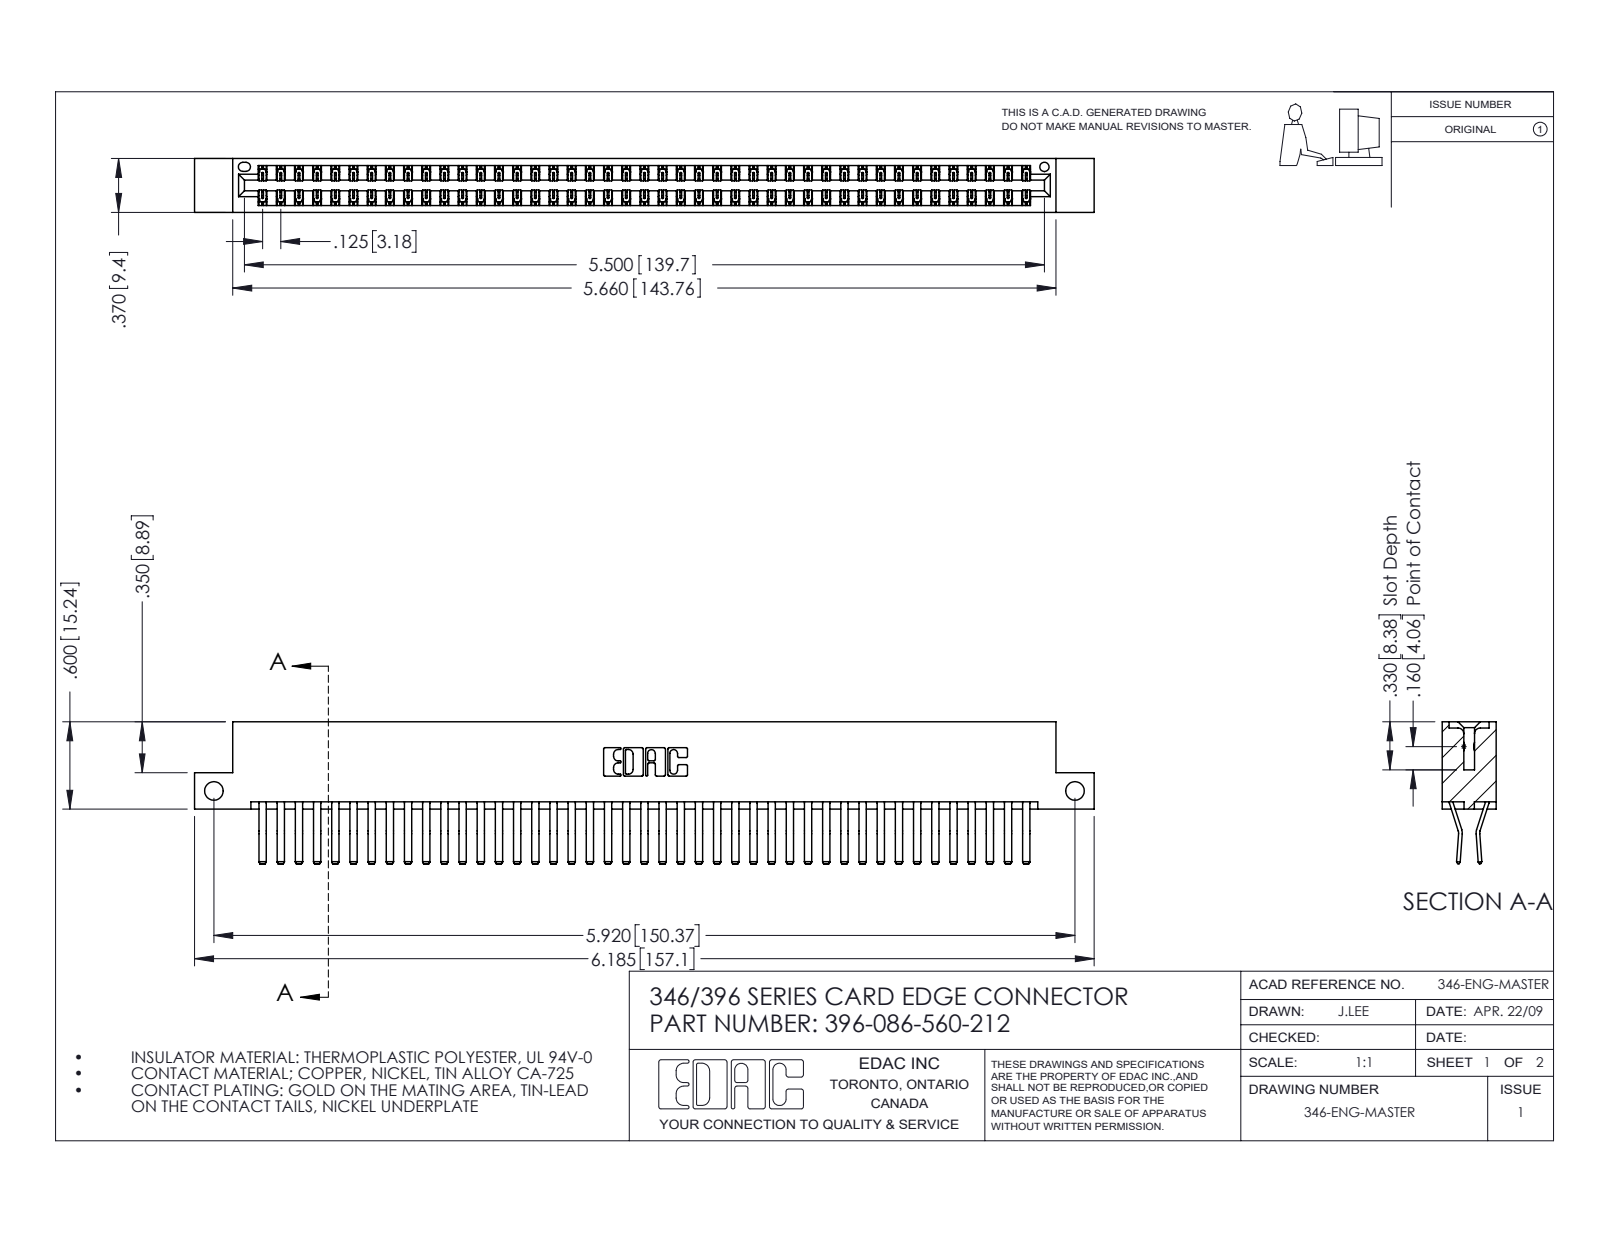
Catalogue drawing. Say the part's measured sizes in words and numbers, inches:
The part is named "396-086-560-212; 345-292-001_560 Tail; 346 Part_Flush Mounting Lugs - Side Mount". Its 3-D file was written by "SolidWorks 2016 (CONFIG_CONTROL_DESIGN)". It is 87 solids with 4766 faces: 3086 planar, 1680 cylindrical and 0 other. Overall it measures 6.185 by 0.975 by 0.37 inches. Its volume is 0.964 cubic inches and its surface area 35.81 square inches. Round holes: 2 of diameter 0.128, 1 of diameter 0.064. Partial cylindrical surfaces (rounded edges, fillets, slot ends): 129 of radius 0.006, 22 of radius 0.01, 6 of radius 0.007, 6 of radius 0.031, 3 of radius 0.026, 2 of radius 0.01, 2 of radius 0.014, 2 of radius 0.022. The main face-to-face distances are 0.048, 0.322, 0.37, 0.025, 0.25, 0.072, 0.298, 0.275, 0.148, 0.222. The hole center spacings are 5.92.
